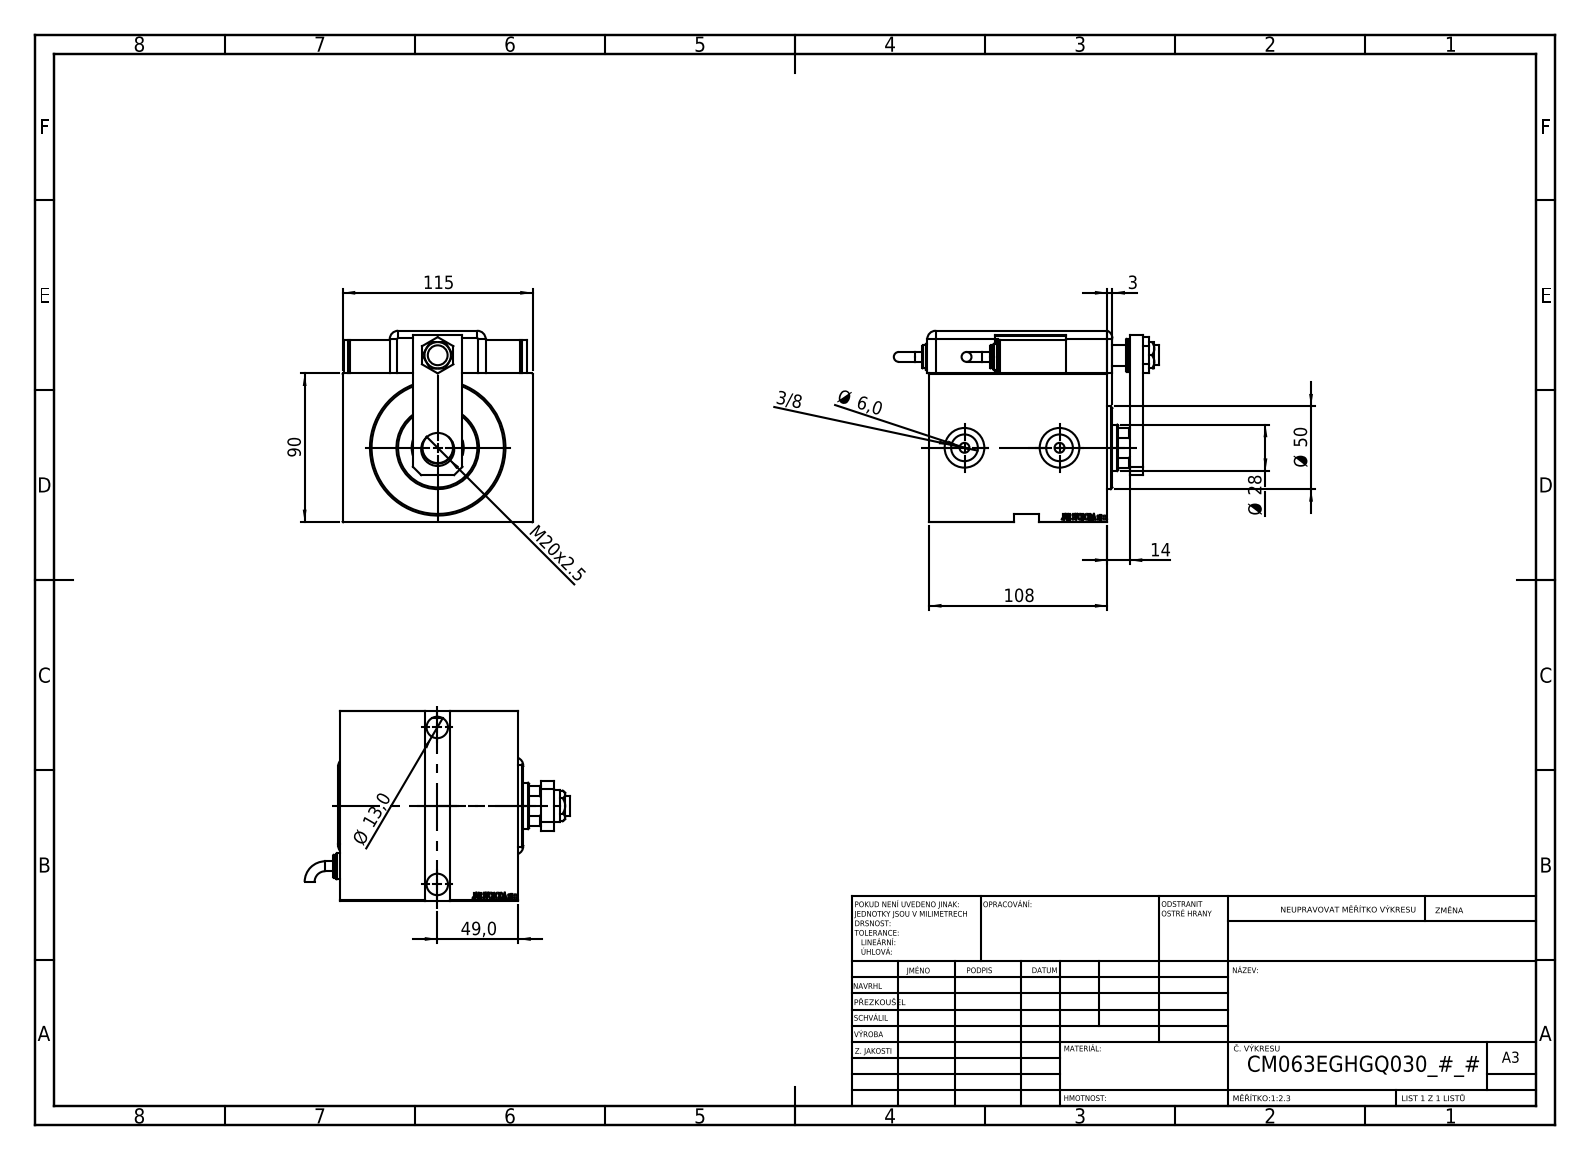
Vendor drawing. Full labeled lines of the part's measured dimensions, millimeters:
Part name (STEP PRODUCT): TYC; NUT_D19; ZARAZKA_Q; MAGNETIC SWITCH Q (+7 more)
STEP written by: SolidWorks 2019 (CONFIG_CONTROL_DESIGN)
Units: millimetres
Bodies: 13 solids, 1230 faces (614 planar, 99 cylindrical, 517 other)
Overall size (bounding box): 160.46 × 115.8 × 115
Volume: 1 160 000 mm³ · Surface area: 187 038 mm²
Round holes (diameter × count): ⌀13 ×3, ⌀4 ×2, ⌀6 ×2, ⌀8 ×2, ⌀16.17 ×2, ⌀19 ×2, ⌀24 ×2, ⌀12 ×1, ⌀14 ×1, ⌀18.5 ×1, ⌀20 ×1, ⌀28 ×1
Round bosses / shafts (diameter × count): ⌀20 ×3, ⌀16 ×2, ⌀14 ×2, ⌀6 ×2, ⌀65 ×1, ⌀50 ×1
Partial cylindrical surfaces — rounded edges, fillets, slot ends (radius × count): R5 ×9, R10 ×1, R13.5 ×1
Main face-to-face distances: 108, 3, 90, 115, 90.5, 17.5, 18.5, 5, 115.8, 25.8
Hole centre spacings: 55.93, 70.91, 1, 20, 56, 57, 57.5, 95
